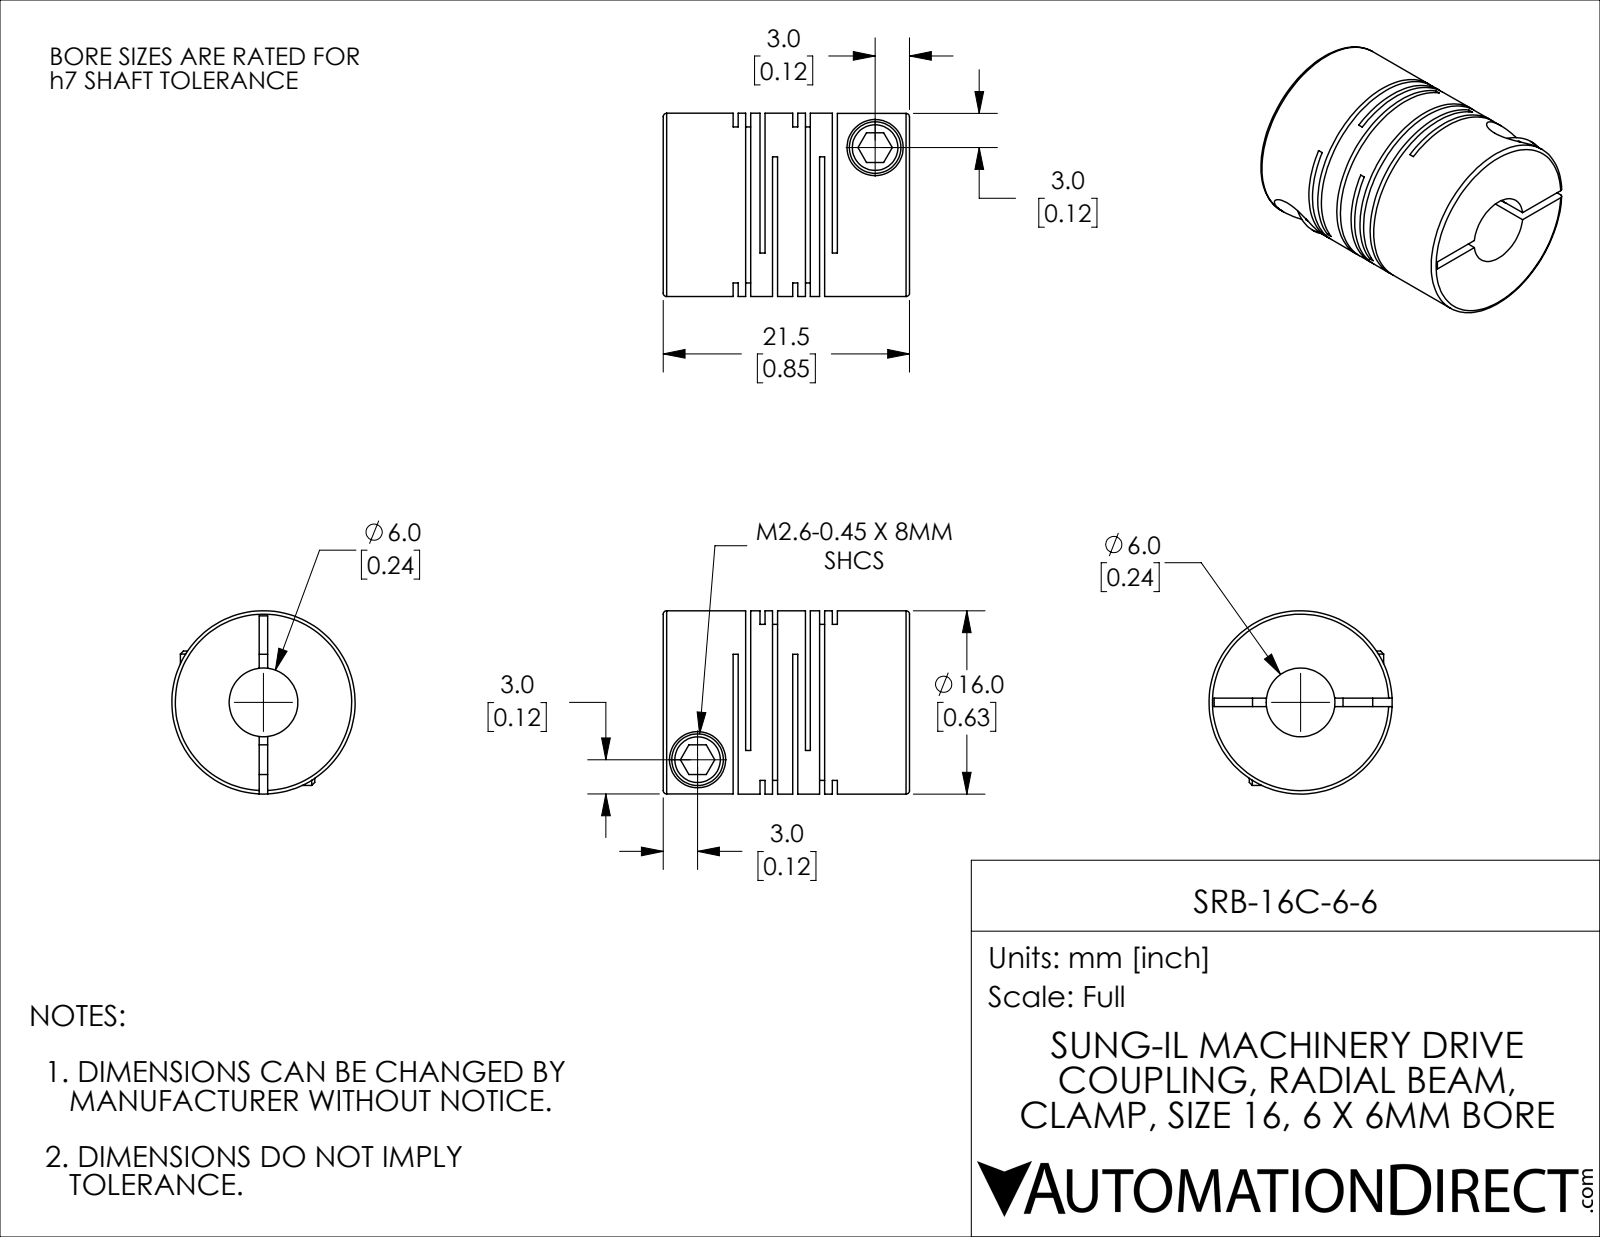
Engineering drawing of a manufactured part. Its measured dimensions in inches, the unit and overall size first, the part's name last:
Units: inches
Overall size (bounding box): 0.846 × 0.63 × 0.63
Round holes (diameter × count): ⌀0.102 ×2, ⌀0.193 ×2, ⌀0.236 ×1
Round bosses / shafts (diameter × count): ⌀0.177 ×2, ⌀0.63 ×1
Main face-to-face distances: 0.017, 0.043, 0.093, 0.205, 0.026, 0.075, 0.188, 0.049, 0.162, 0.113
Volume: 0.186 in³ · Surface area: 6.578 in²
Bodies: 1 solid, 114 faces (60 planar, 42 cylindrical, 12 other)
Part name (STEP PRODUCT): SRB-16C-6-6
STEP written by: SolidWorks 2021 (CONFIG_CONTROL_DESIGN)
